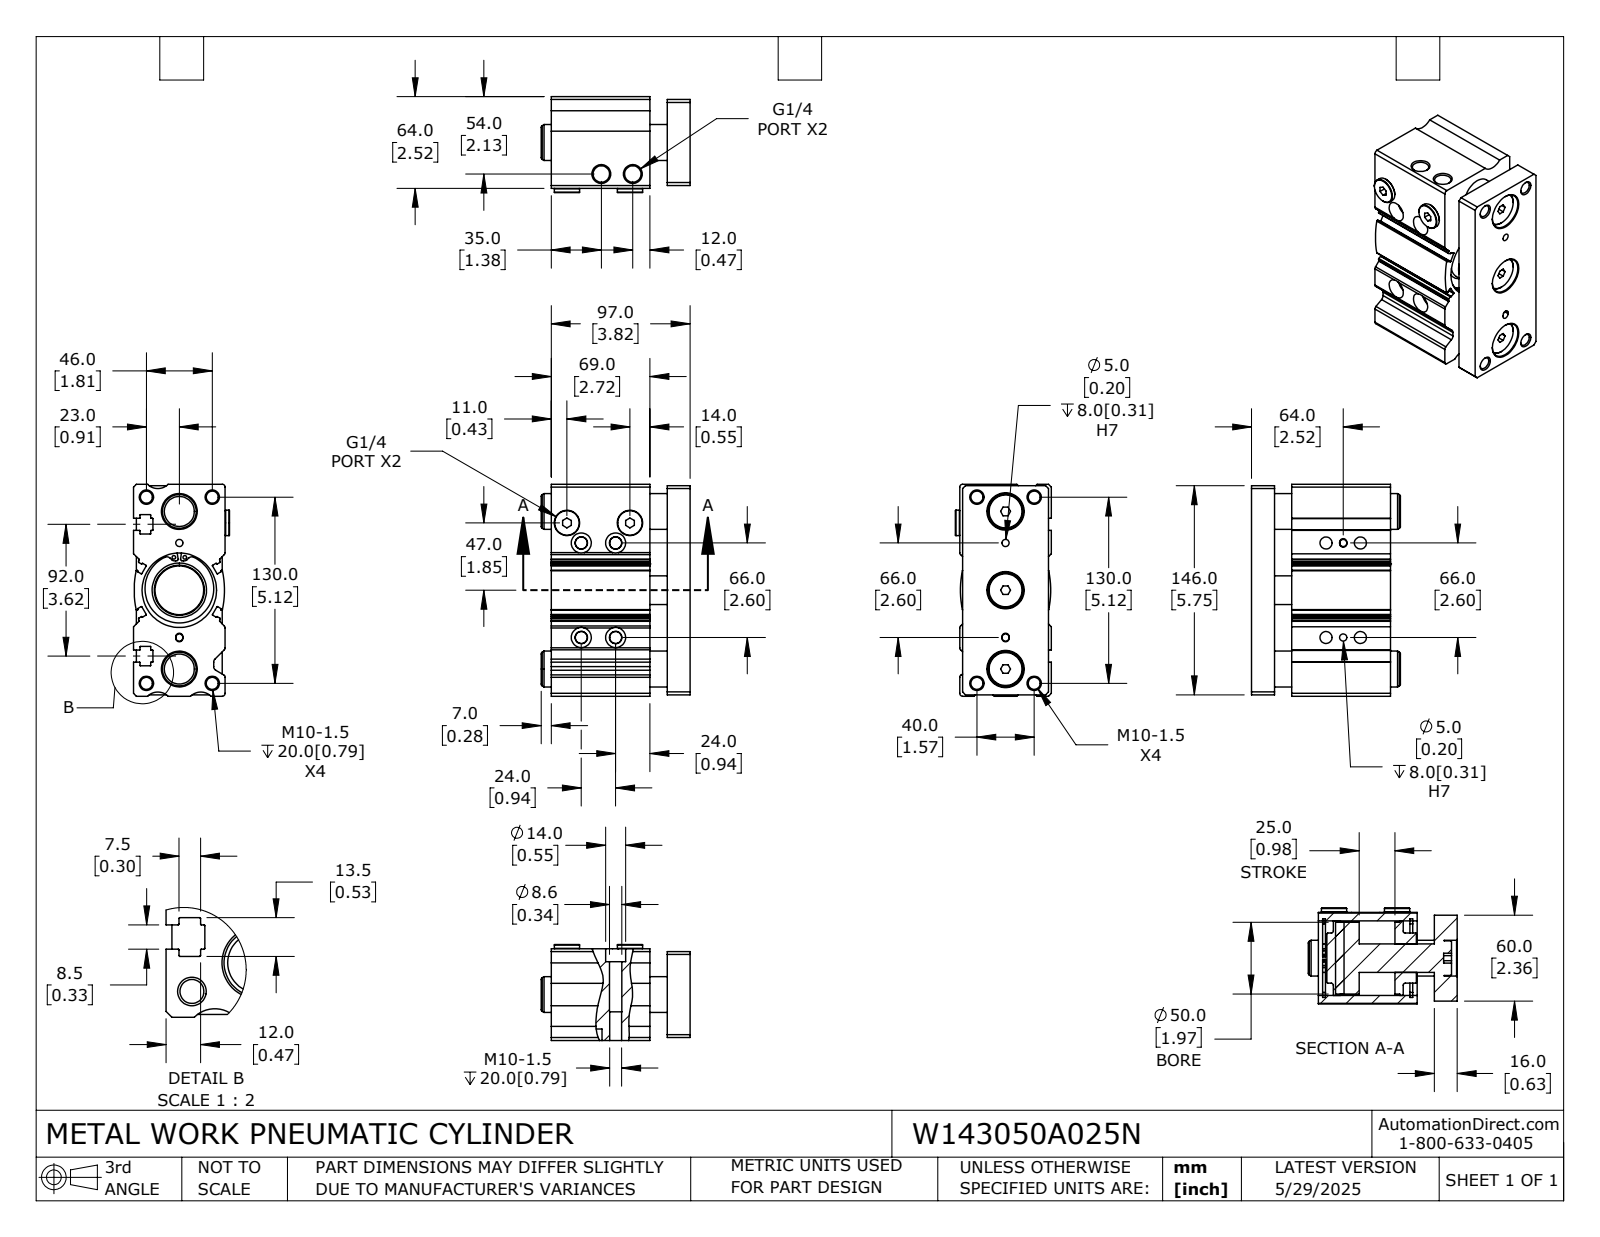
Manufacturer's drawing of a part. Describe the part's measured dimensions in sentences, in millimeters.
The part is named "W143050A025N_ROD; W143050A025N_BODY; W143050A025N". Its 3-D file was written by "SolidWorks 2024 (CONFIG_CONTROL_DESIGN)". It is 6 solids with 466 faces: 186 planar, 224 cylindrical and 56 other. Overall it measures 148 by 104 by 67 millimeters. Its volume is 661 492 cubic millimeters and its surface area 150 743 square millimeters. Round holes: 12 of diameter 8.38, 4 of diameter 2.5, 4 of diameter 5, 4 of diameter 8.6, 4 of diameter 14, 3 of diameter 25, 2 of diameter 11.44, 2 of diameter 48, 1 of diameter 20. Round bosses or shafts: 3 of diameter 24, 2 of diameter 17.7, 1 of diameter 55, 1 of diameter 52, 1 of diameter 50, 1 of diameter 35. Partial cylindrical surfaces (rounded edges, fillets, slot ends): 44 of radius 0.3, 12 of radius 0.5, 10 of radius 3, 6 of radius 2, 6 of radius 68, 4 of radius 1, 4 of radius 2.5, 3 of radius 10. The main face-to-face distances are 12, 69, 16, 81, 28, 2, 97, 64, 62, 6. The hole center spacings are 3, 10.76, 12, 22.08, 22.36, 23.27, 24.45, 25.08.
